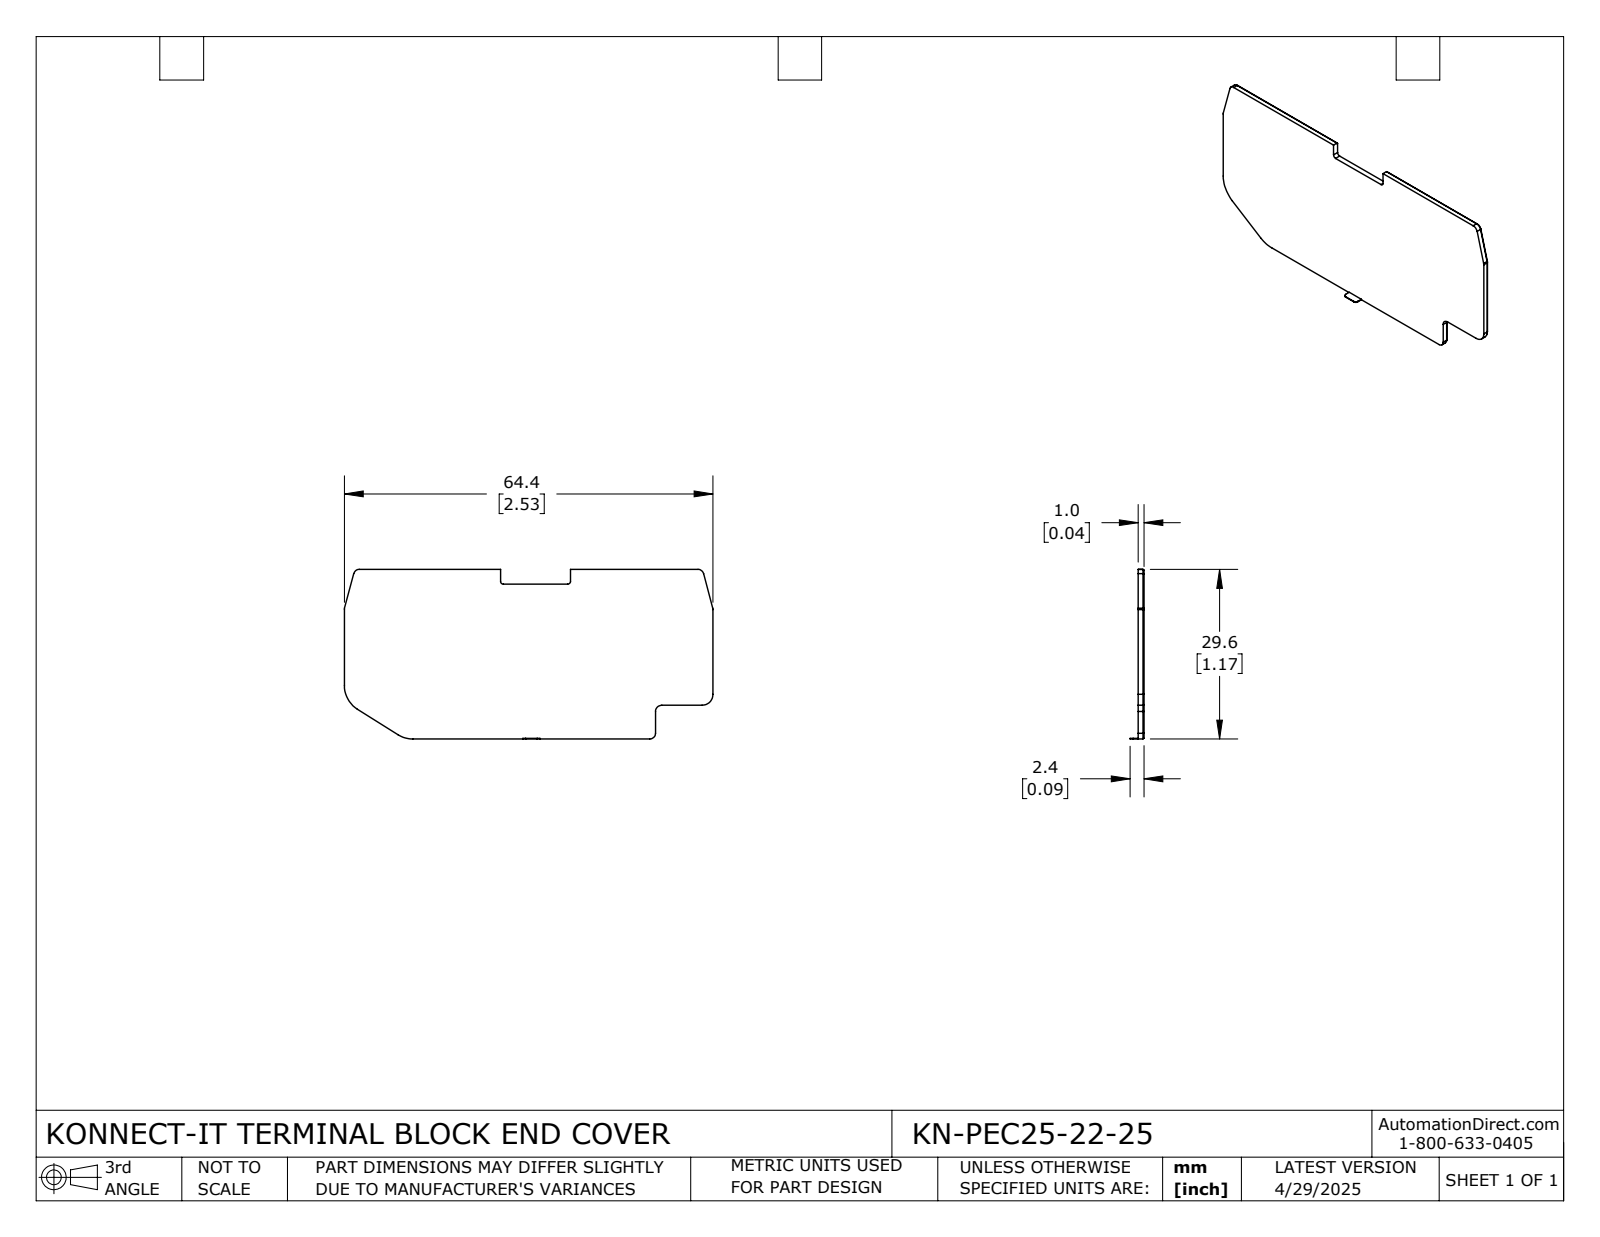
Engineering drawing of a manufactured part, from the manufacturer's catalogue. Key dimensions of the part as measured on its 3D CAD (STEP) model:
Part name (STEP PRODUCT): KN-PEC25-22-25
STEP written by: SolidWorks 2024 (CONFIG_CONTROL_DESIGN)
Units: millimetres
Bodies: 1 solid, 52 faces (30 planar, 22 cylindrical, 0 other)
Overall size (bounding box): 64.37 × 29.61 × 2.4
Volume: 1 763 mm³ · Surface area: 3 721 mm²
Partial cylindrical surfaces — rounded edges, fillets, slot ends (radius × count): R0.9 ×5, R1 ×5, R0.5 ×4, R4.8 ×2, R4.9 ×2, R1.1 ×1, R1.2 ×1, R1.8 ×1
Main face-to-face distances: 1, 29.61, 29.51, 0.85, 64.37, 27.02, 2.59, 26.92, 29.41, 2.49
